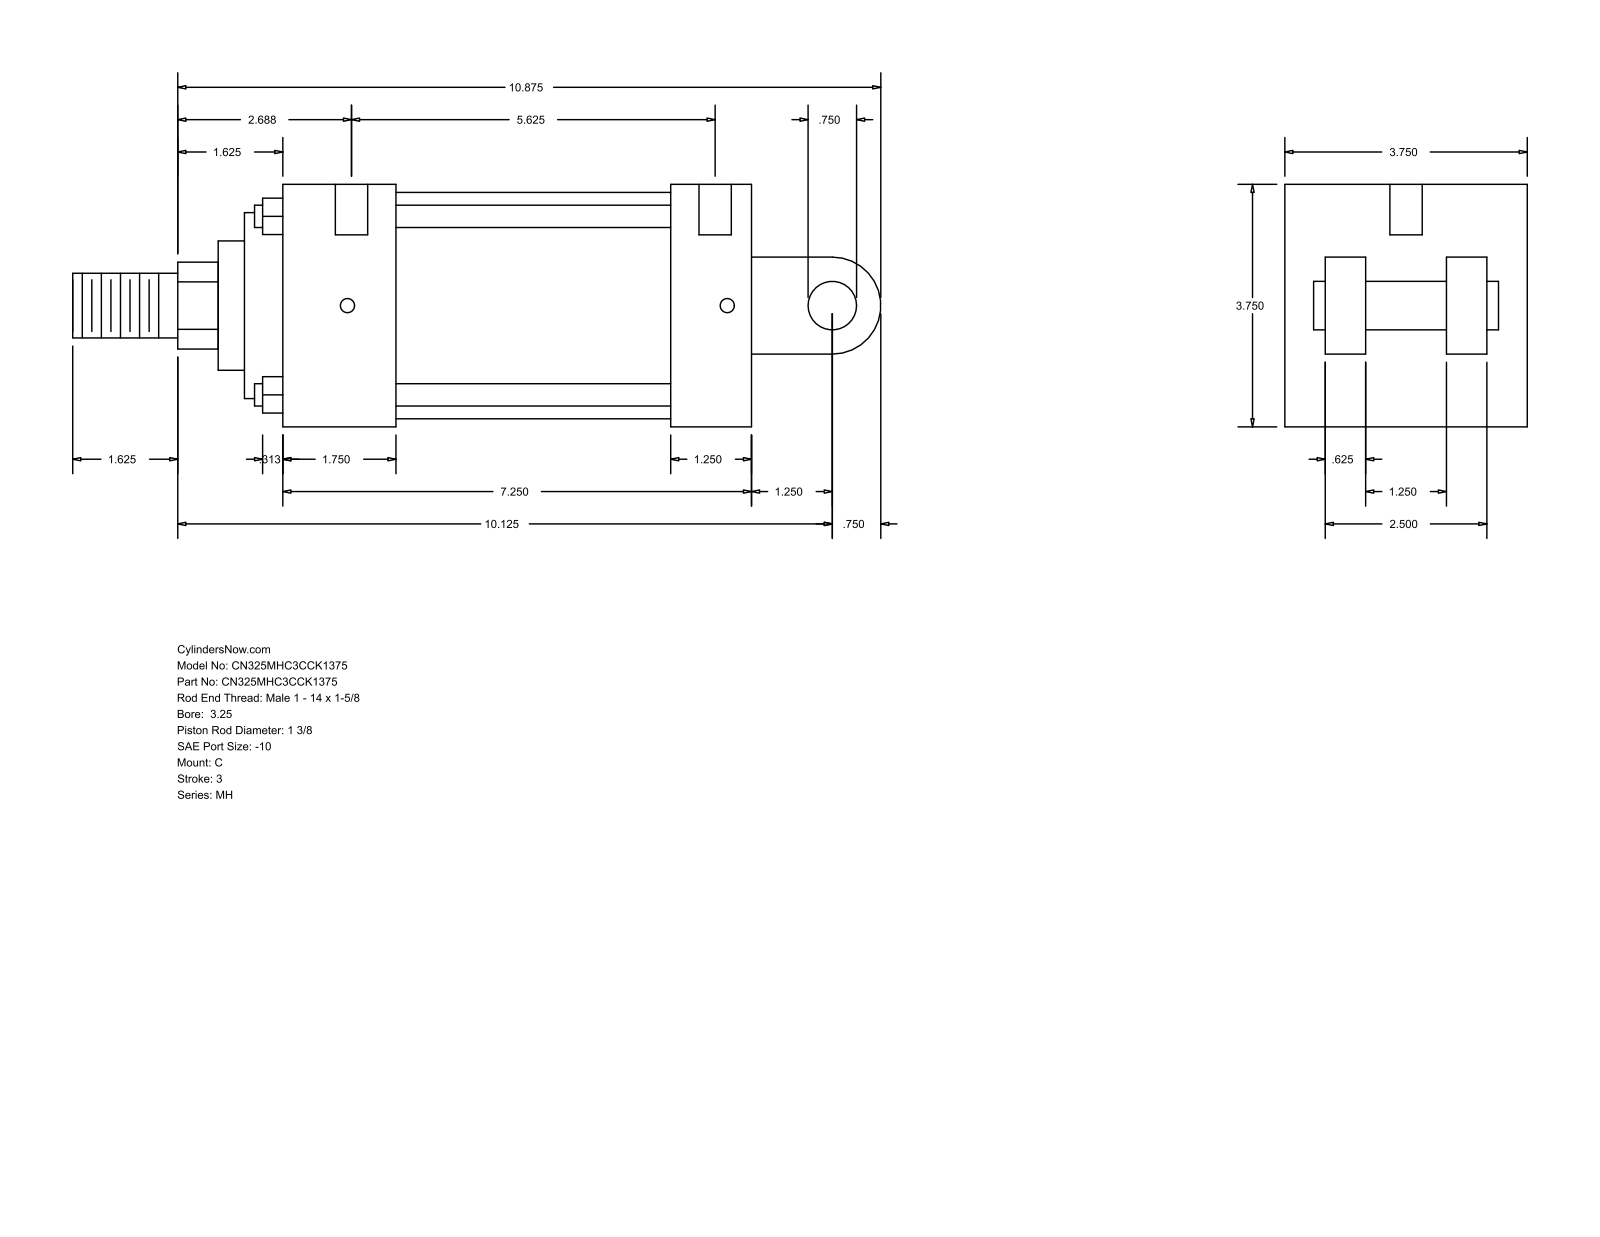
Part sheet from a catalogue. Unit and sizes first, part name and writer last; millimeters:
Units: millimetres
Overall size (bounding box): 317.5 × 95.25 × 95.25
Round holes (diameter × count): ⌀5.56 ×4, ⌀12.7 ×2
Round bosses / shafts (diameter × count): ⌀8.76 ×4, ⌀88.9 ×1, ⌀73.03 ×1, ⌀50.8 ×1, ⌀34.92 ×1, ⌀25.4 ×1, ⌀19.05 ×1
Partial cylindrical surfaces — rounded edges, fillets, slot ends (radius × count): R17.06 ×1, R19.05 ×1
Main face-to-face distances: 95.24, 15.87, 63.5, 184.16, 31.74, 79.37, 47.63, 44.45, 152.41, 107.96
Hole centre spacings: 149.23, 1.59, 4.76, 142.88, 144.47, 147.64
Bodies: 0 solids, 101 faces (71 planar, 30 cylindrical, 0 other)
Part name (STEP PRODUCT): MH_C__0325_1.375
STEP written by: GSSL Pune (CONFIG_CONTROL_DESIGN)
